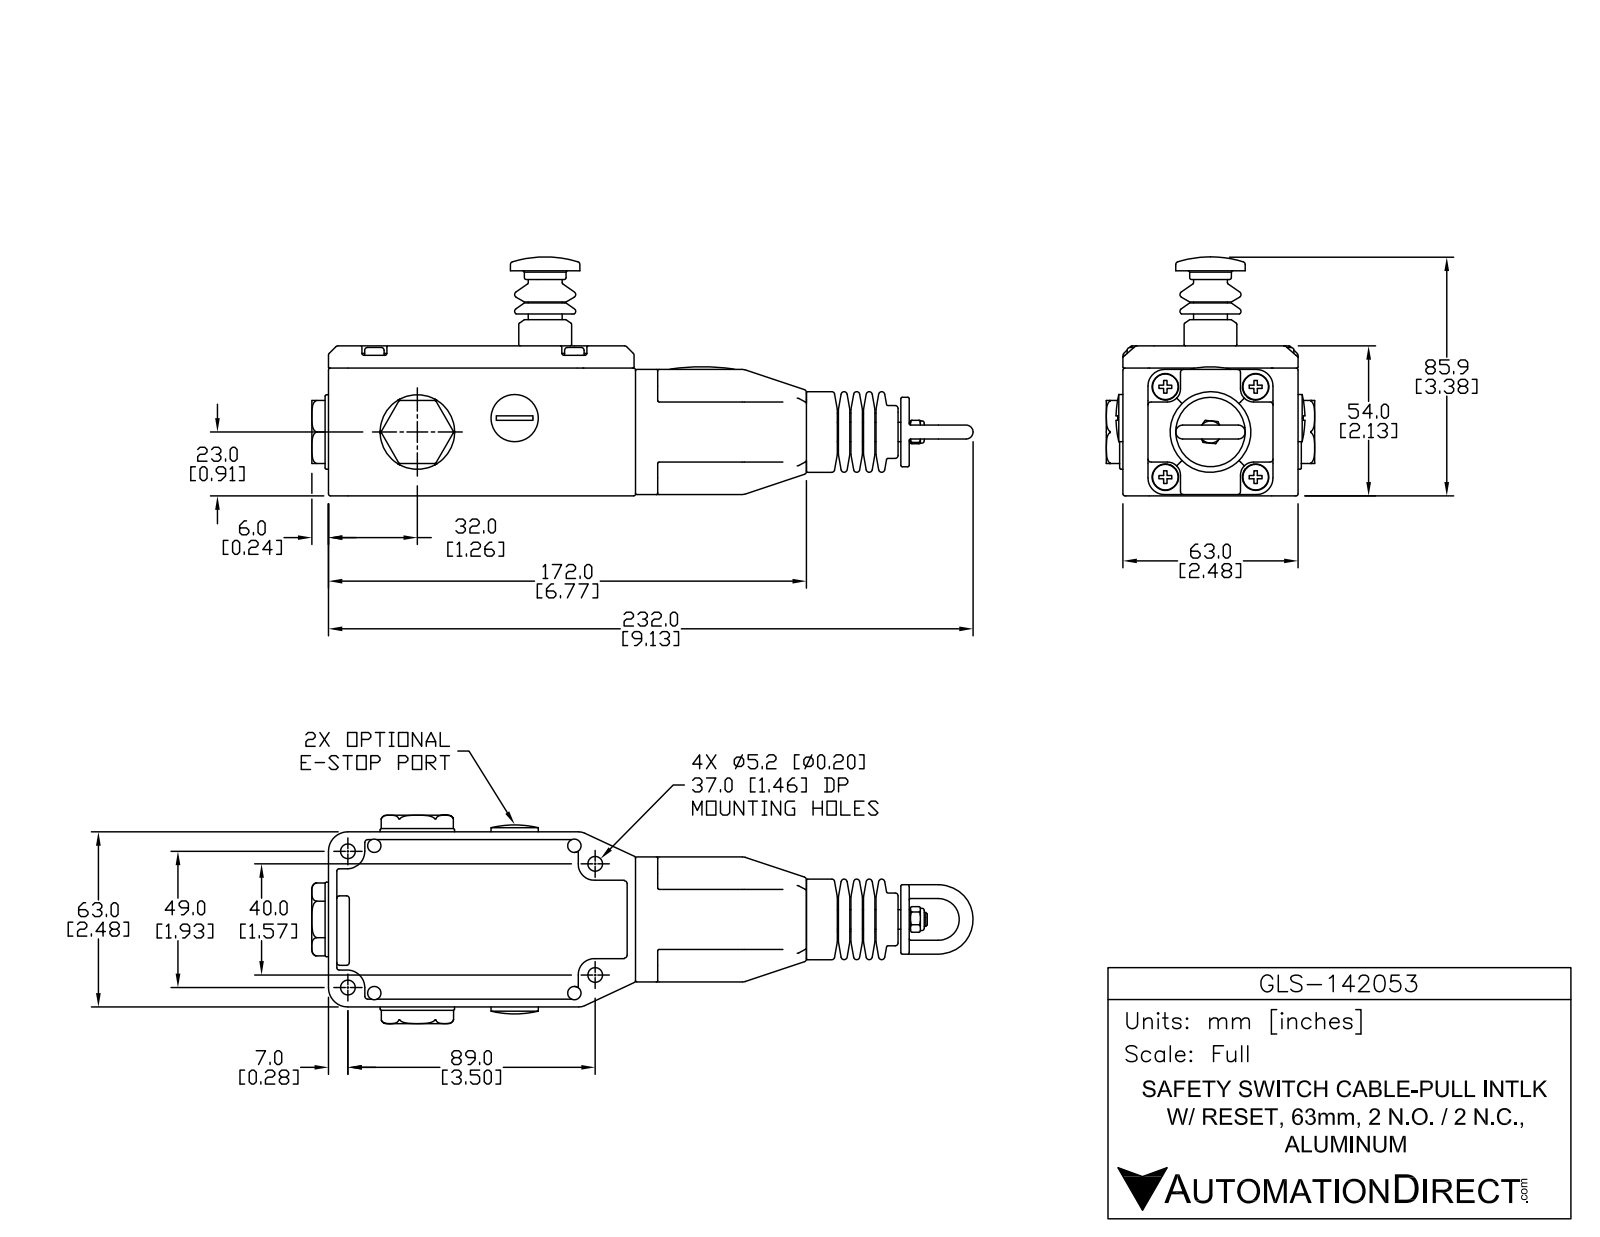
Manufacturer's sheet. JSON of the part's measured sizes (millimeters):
{"part_name": "GLS-142053", "step_written_by": "SolidWorks 2013 (AUTOMOTIVE_DESIGN)", "units": "millimeters", "bodies": {"solids": 1, "faces": 617, "planar": 210, "cylindrical": 201, "other": 206}, "overall_size": [238, 102.3, 86], "volume_mm3": 492222, "surface_area_mm2": 64589, "round_holes": [[4.75, 4], [9.5, 4], [5, 2], [5.2, 2], [34, 1]], "round_bosses_or_shafts": [[9.2, 4], [6, 4], [26.8, 2], [25, 2], [19, 2], [12, 2], [5, 2], [40, 1]], "partial_cylinders_radius": [[0.5, 42], [0.75, 20], [1.1, 6], [4, 4], [4.5, 4], [4.8, 4], [16, 4], [5.8, 2]], "face_to_face_distances": [53.68, 63, 54, 9, 11.7, 33.3, 45, 4.5, 49.5, 0.32], "hole_center_spacings": [9.6, 9.62, 32.4, 32.6, 45.96, 46.61, 51.39, 52]}
